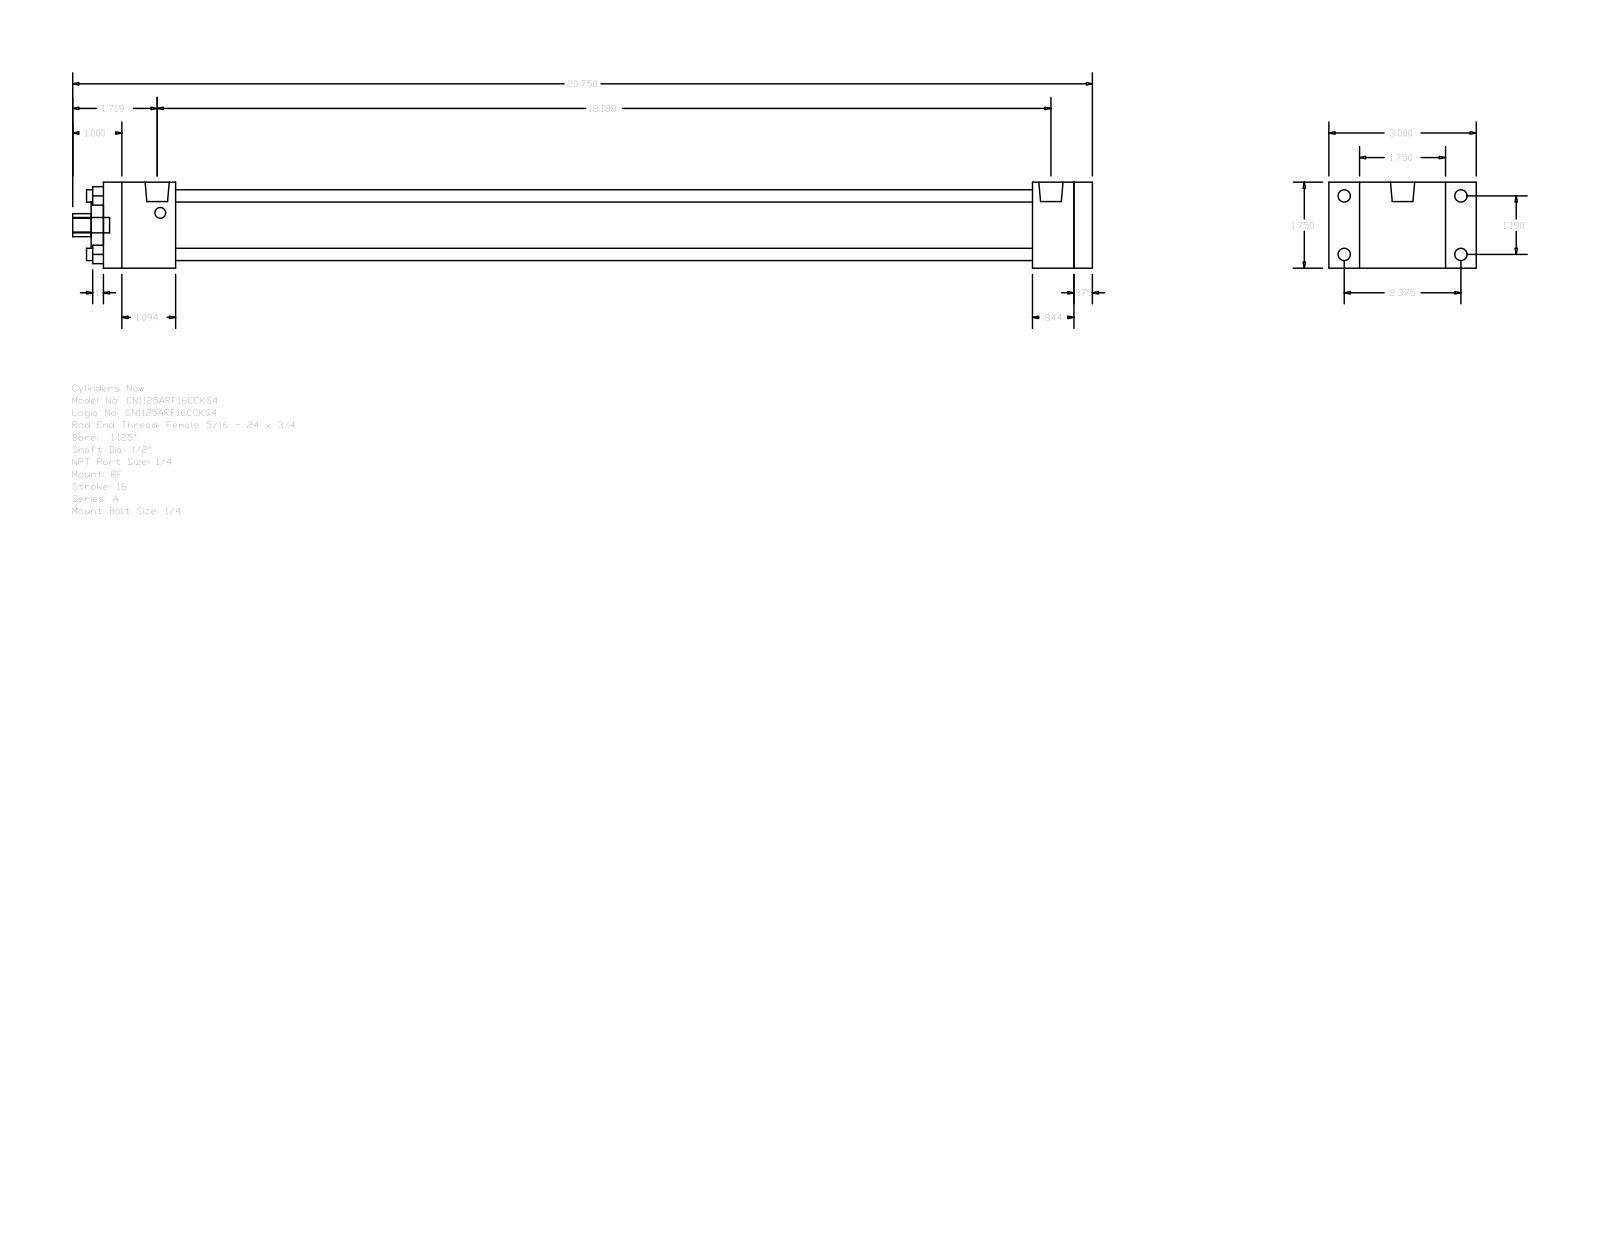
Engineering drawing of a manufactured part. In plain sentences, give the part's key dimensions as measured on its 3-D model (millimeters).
The part is named "A_RF__0112_0.5". Its 3-D file was written by "GSSL Pune (CONFIG_CONTROL_DESIGN)". It is 0 solids with 92 faces: 64 planar, 28 cylindrical and 0 other. Overall it measures 527.05 by 76.2 by 44.45 millimeters. Round holes: 4 of diameter 6.35, 1 of diameter 12.7, 1 of diameter 23.81, 1 of diameter 31.88. Round bosses or shafts: 4 of diameter 6.35, 4 of diameter 5.56, 2 of diameter 12.49, 1 of diameter 7.94. Partial cylindrical surfaces (rounded edges, fillets, slot ends): 1 of radius 5.94. The main face-to-face distances are 44.46, 9.53, 511.17, 501.64, 37.3, 480.21, 442.91, 464.34, 473.87, 21.43. The hole center spacings are 21.37, 30.22, 42.74.
